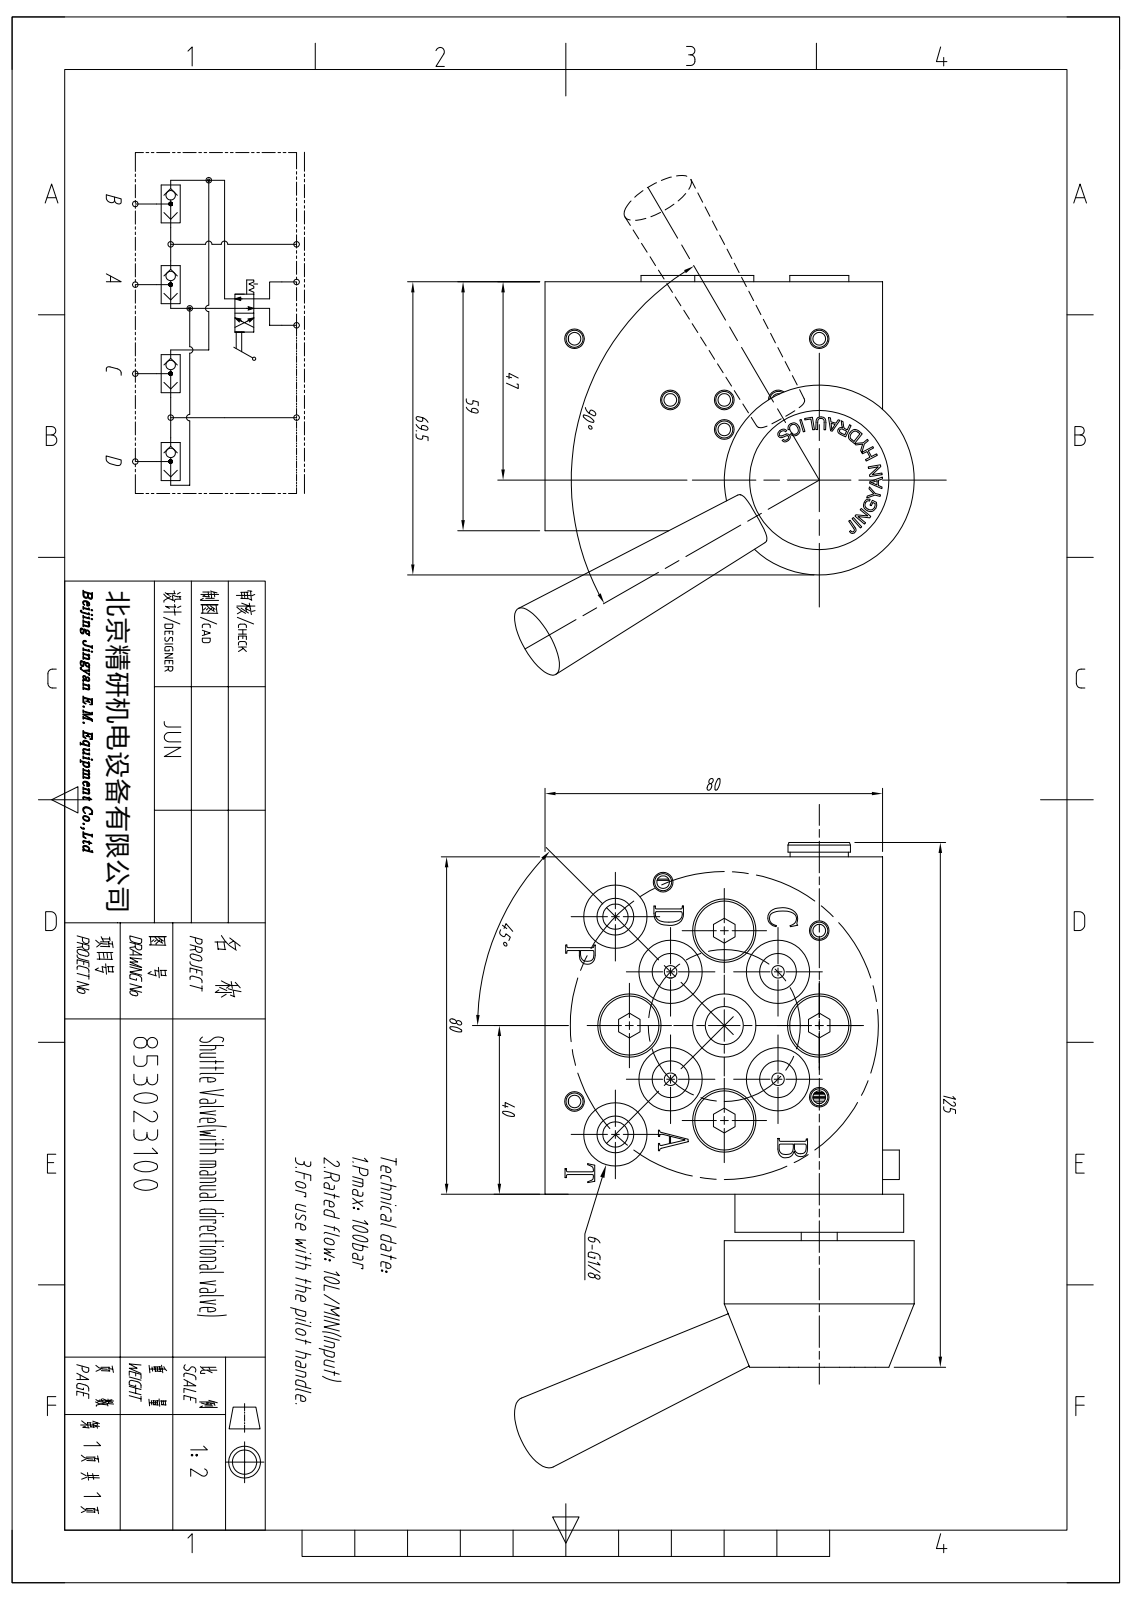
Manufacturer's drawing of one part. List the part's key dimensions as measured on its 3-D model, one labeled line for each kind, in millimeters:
Part name (STEP PRODUCT): shuttle valve 853023100
STEP written by: SolidWorks 2022 (AUTOMOTIVE_DESIGN)
Units: millimetres
Bodies: 0 solids, 511 faces (252 planar, 106 cylindrical, 153 other)
Overall size (bounding box): 148.28 × 111.75 × 90.76
Round holes (diameter × count): ⌀4.05 ×27, ⌀15 ×11, ⌀8.7 ×10, ⌀20.5 ×6, ⌀5 ×3, ⌀4 ×2, ⌀6 ×2, ⌀3 ×1, ⌀3.3 ×1, ⌀7.6 ×1, ⌀9 ×1, ⌀10.5 ×1
Round bosses / shafts (diameter × count): ⌀14 ×4, ⌀45 ×1, ⌀40 ×1, ⌀15 ×1, ⌀14.8 ×1, ⌀13.8 ×1
Partial cylindrical surfaces — rounded edges, fillets, slot ends (radius × count): R2.6 ×4
Main face-to-face distances: 79.97, 80, 58.99, 2, 56.99, 11, 91, 9, 89, 30
Hole centre spacings: 26.02, 54.77, 22.5, 37.46, 31.82, 16.05, 54.78, 51.62
